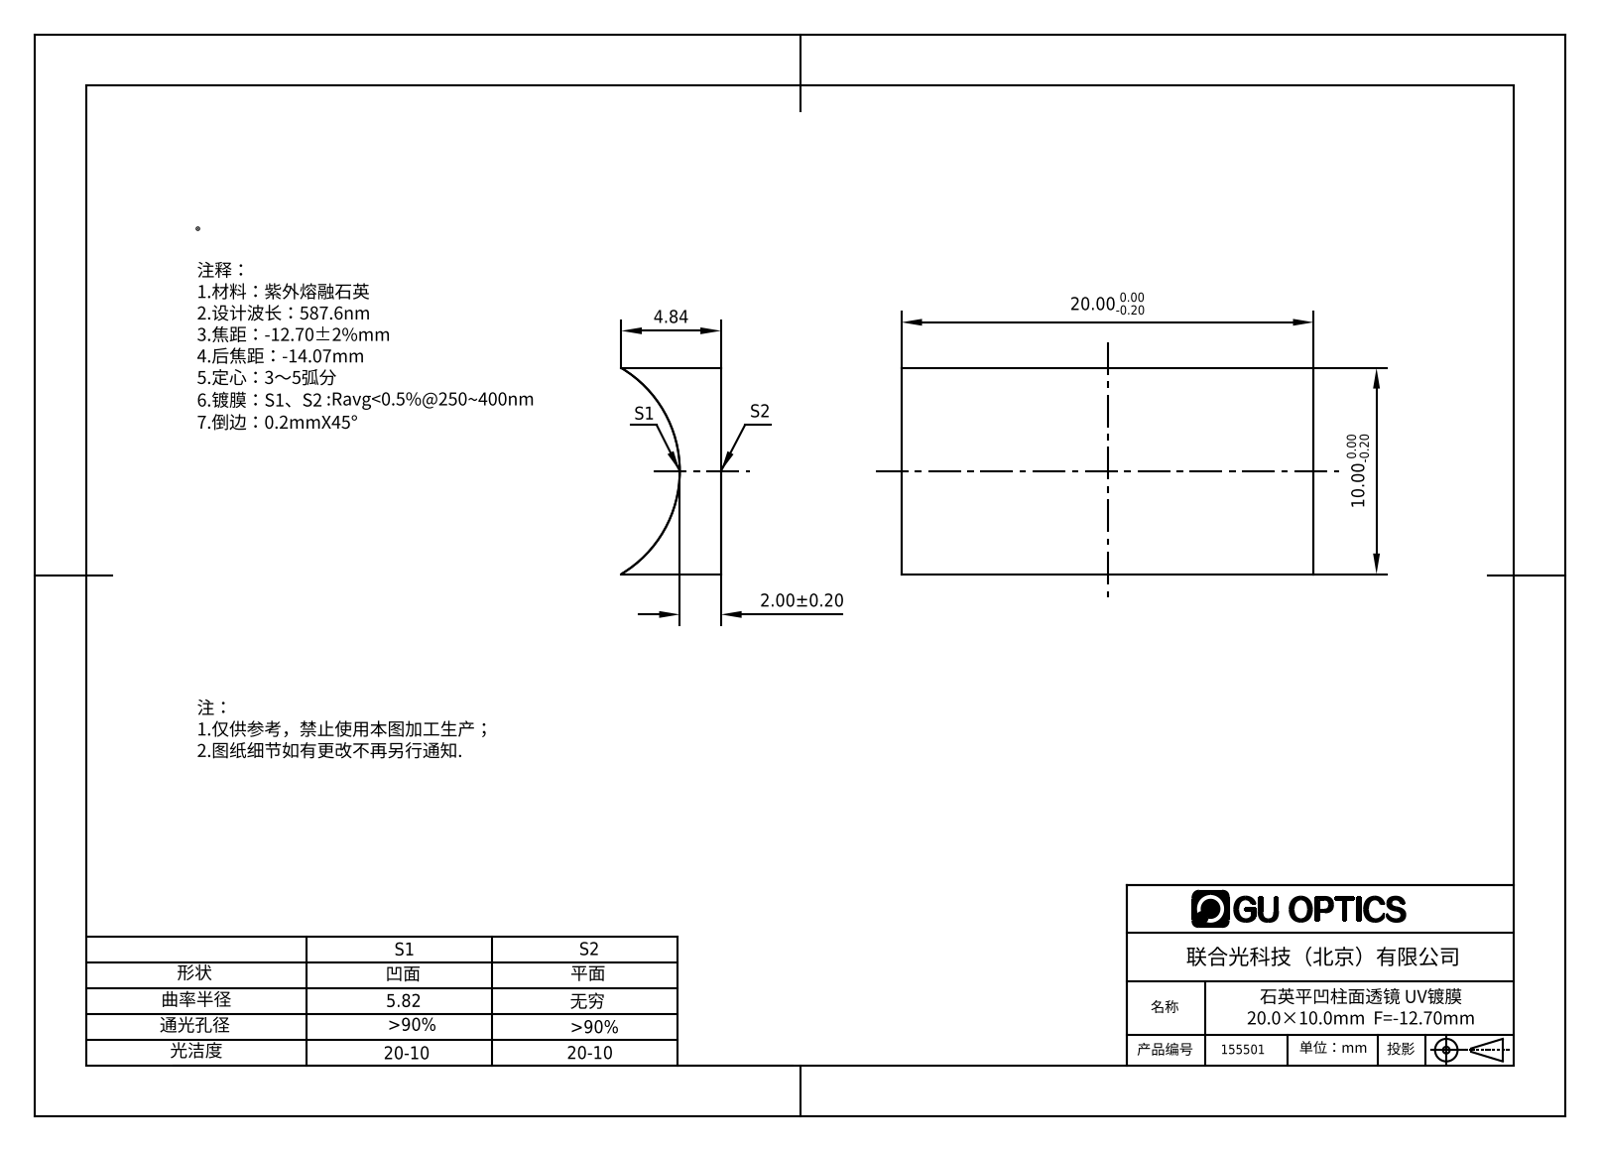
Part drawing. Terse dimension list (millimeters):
name: 155475
written by: SolidWorks 2016 (AUTOMOTIVE_DESIGN)
unit: mm
bodies: 1 solid, 6 faces (5 planar, 1 cylindrical, 0 other)
size: 20 × 10 × 4.84
volume: 566 mm³; area: 691 mm²
rounds: 1× R5.82
face distances: 10, 20
